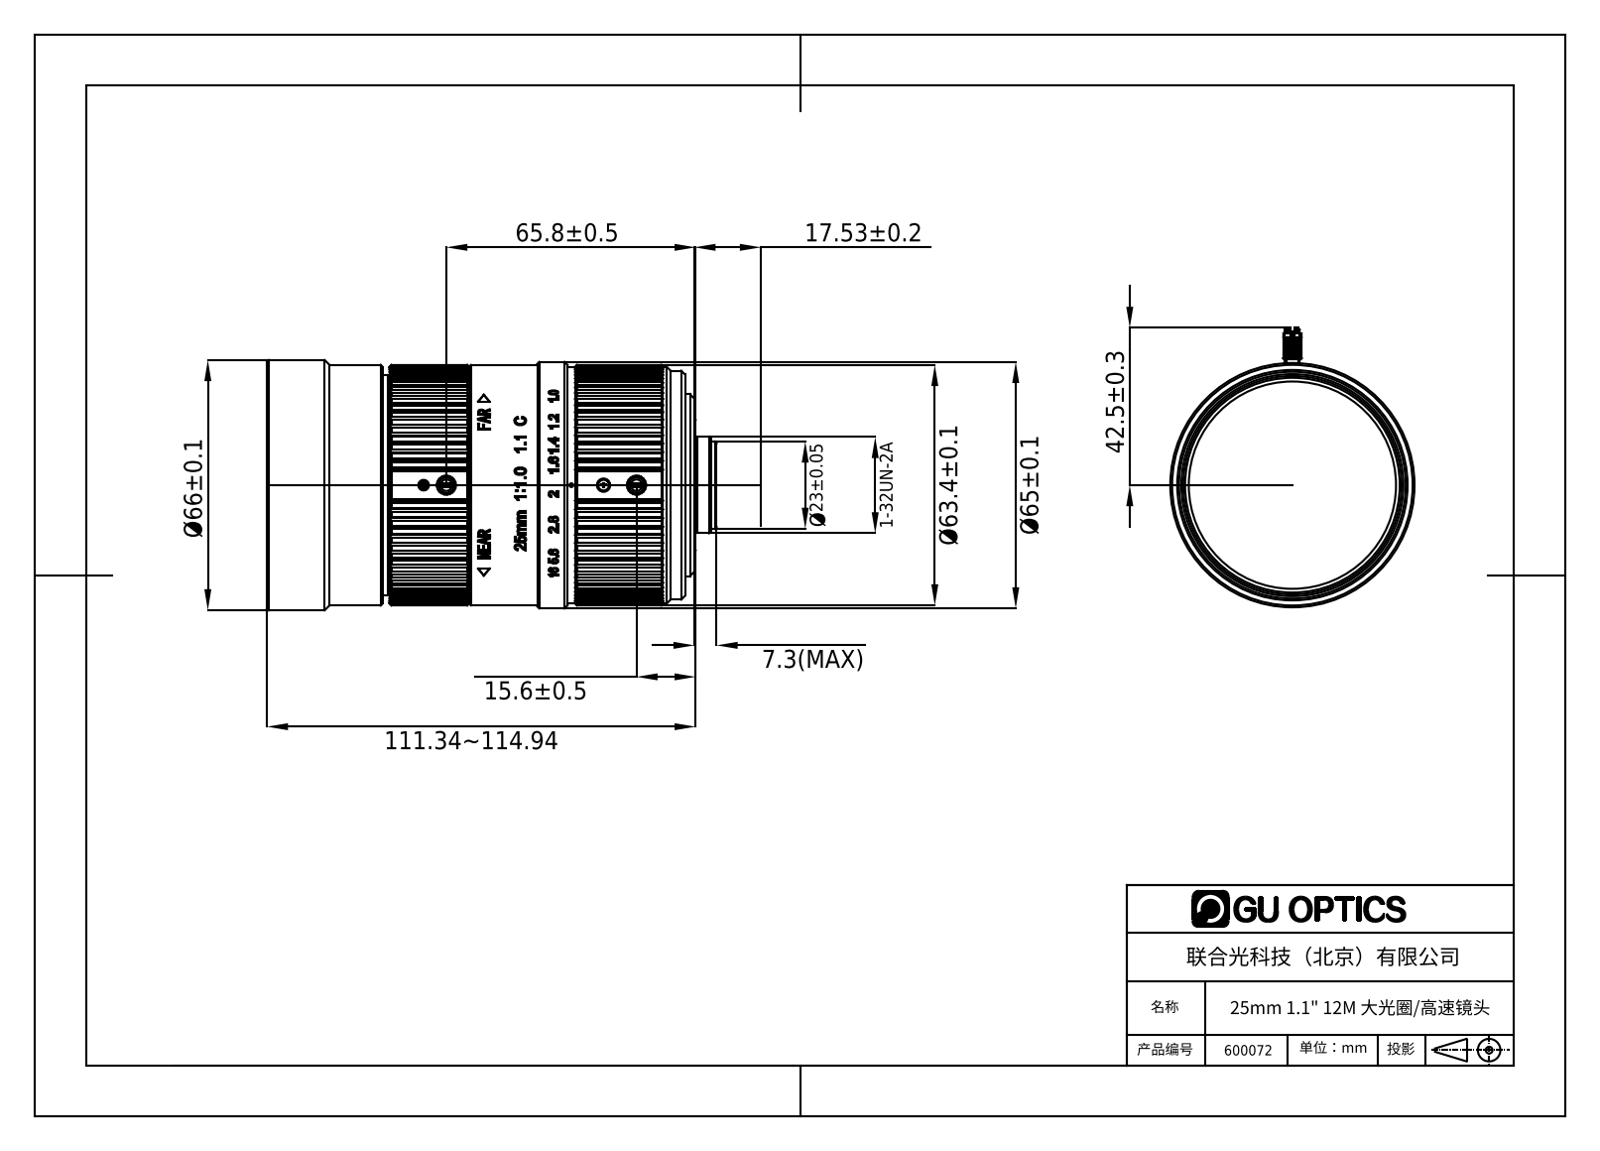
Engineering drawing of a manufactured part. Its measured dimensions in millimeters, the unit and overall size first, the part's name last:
Units: millimetres
Overall size (bounding box): 118.68 × 75.5 × 66
Round holes (diameter × count): ⌀1.6 ×16, ⌀1.8 ×7, ⌀2.8 ×7, ⌀1.25 ×4, ⌀2.4 ×3, ⌀2.5 ×3, ⌀3 ×3, ⌀4.3 ×3, ⌀1 ×1, ⌀3.5 ×1, ⌀20 ×1, ⌀21.2 ×1
Round bosses / shafts (diameter × count): ⌀2.5 ×7, ⌀2 ×6, ⌀1.6 ×4, ⌀3.8 ×3, ⌀3.5 ×3, ⌀4 ×2, ⌀66 ×1, ⌀65 ×1
Partial cylindrical surfaces — rounded edges, fillets, slot ends (radius × count): R2.5 ×2, R29.75 ×1, R31.67 ×1, R32.47 ×1
Main face-to-face distances: 1, 2, 100, 31, 0.5, 3, 0.8, 102, 3.8, 2.5
Hole centre spacings: 30, 42.42, 2.3, 3.7, 6, 20, 34.64, 50.2
Volume: 93 738 mm³ · Surface area: 102 886 mm²
Bodies: 31 solids, 2453 faces (841 planar, 784 cylindrical, 828 other)
Part name (STEP PRODUCT): ǰѹȦ_1; 导套_2; 镜片+隔圈111_3; 连接座_1 (+8 more)
STEP written by: SolidWorks 2020 (CONFIG_CONTROL_DESIGN)
